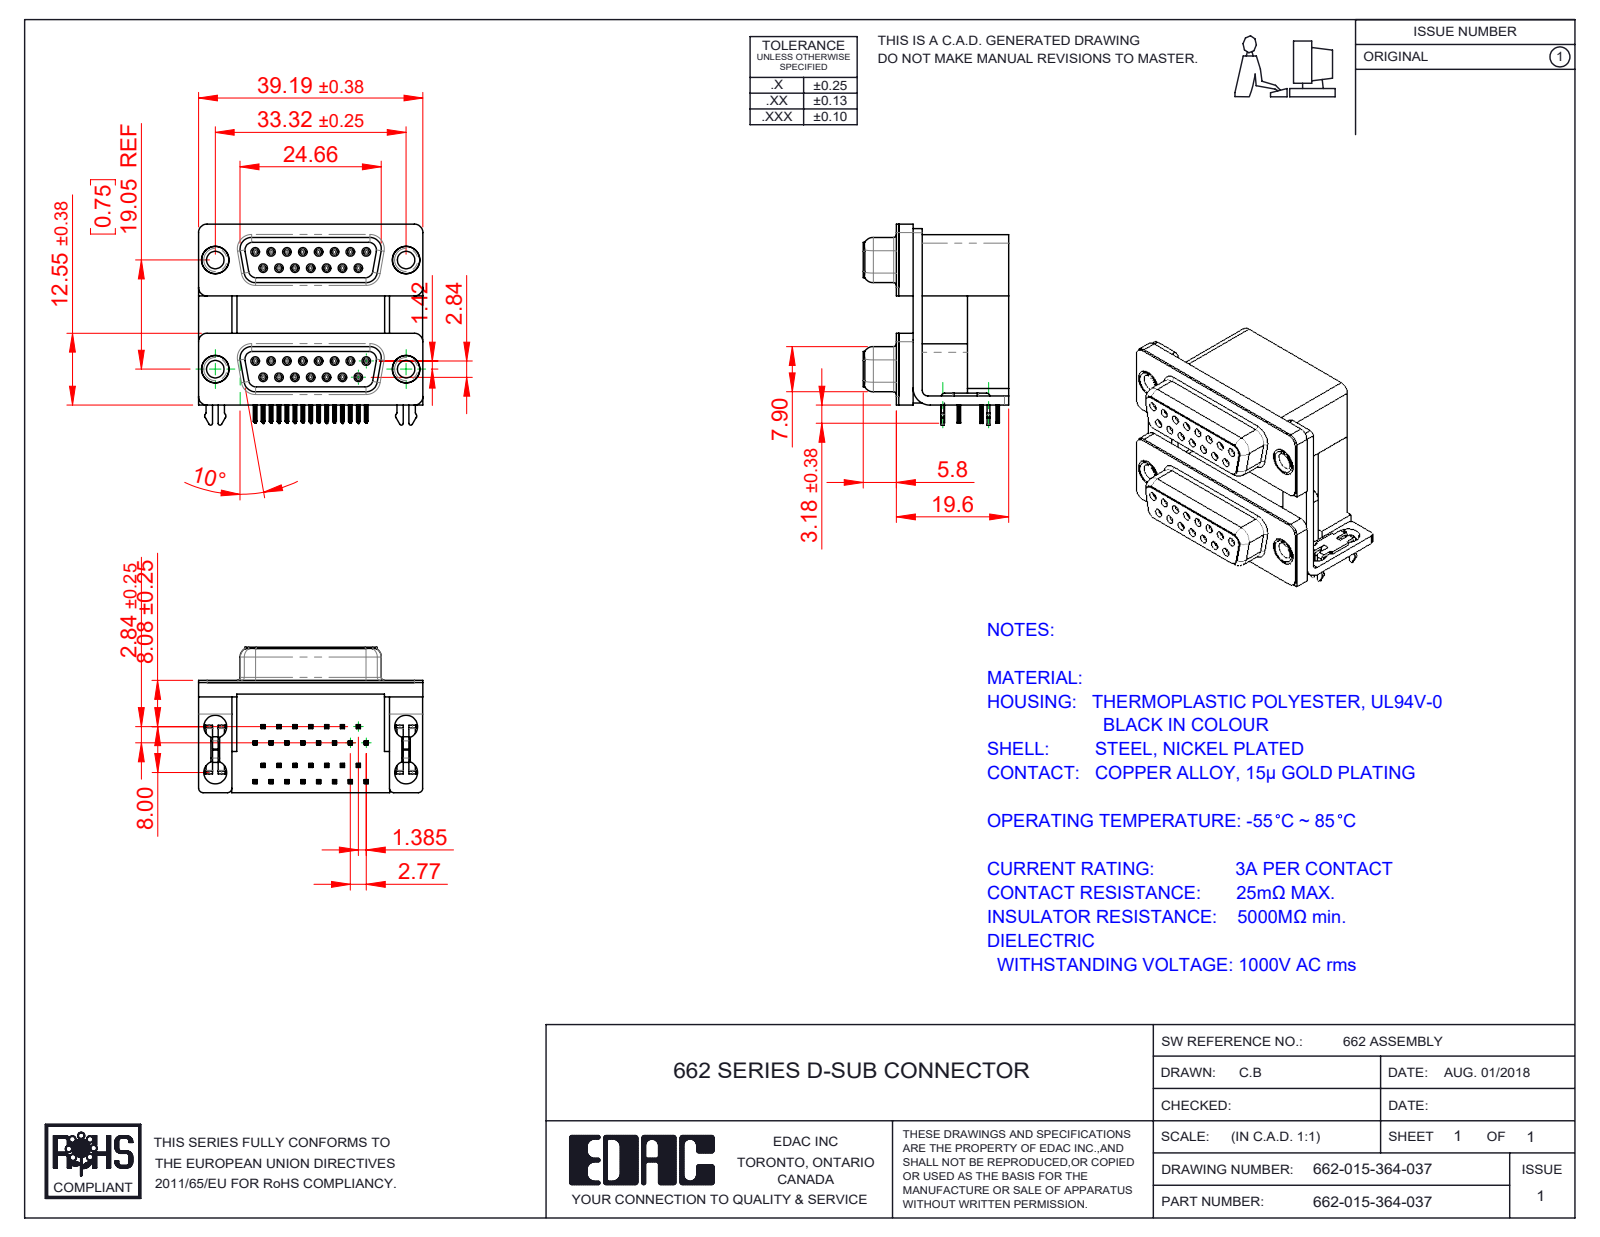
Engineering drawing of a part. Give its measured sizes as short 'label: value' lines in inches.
name: 662 Housing Lower_15 Contacts; 662 Contact Bottom Lower; 662 Housing Spacer_15 Contacts M; 662 Contact Top Lower (+8 more)
written by: SolidWorks 2020 (CONFIG_CONTROL_DESIGN)
unit: in
bodies: 43 solids, 4930 faces (2298 planar, 1188 cylindrical, 1444 other)
size: 1.543 × 1.382 × 1
volume: 0.976 in³; area: 28.1 in²
holes: 30× ⌀0.031, 30× ⌀0.035, 8× ⌀0.157, 4× ⌀0.12, 4× ⌀0.138, 4× ⌀0.189, 4× ⌀0.197
bosses: 30× ⌀0.047, 4× ⌀0.193, 4× ⌀0.187, 4× ⌀0.152
rounds: 242× R0.004, 120× R0.006, 60× R0.014, 30× R0.013, 16× R0.053, 16× R0.059, 14× R0.011, 12× R0.02
face distances: 0.75, 0.016, 0.756, 0.472, 0.098, 0.657, 0.283, 0.374, 0.114, 0.488
hole spacings: 0.124, 0.758, 0.109, 0.781, 0.218, 0.327, 0.75, 0.818
